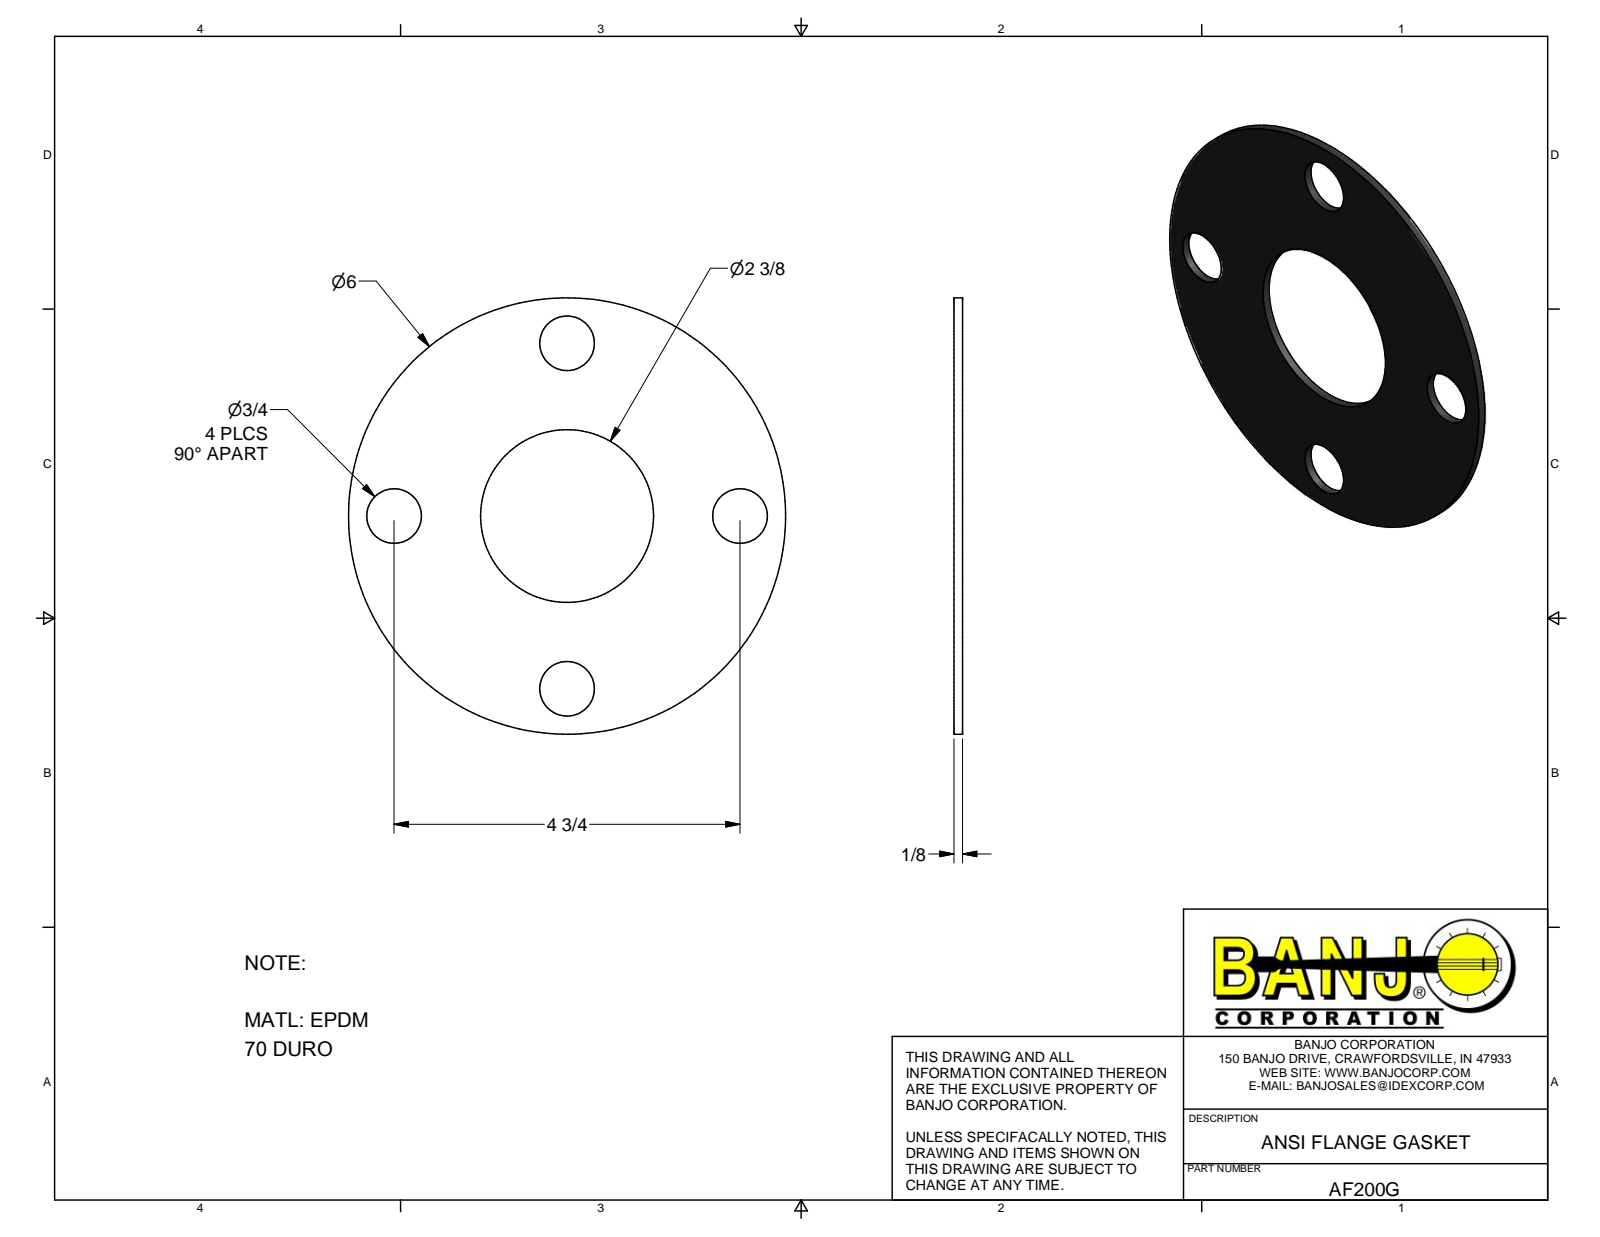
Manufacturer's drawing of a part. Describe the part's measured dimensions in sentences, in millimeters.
The part is named "AF200G". Its 3-D file was written by "Autodesk Inventor 2014 (AUTOMOTIVE_DESIGN)". It is 1 solid with 8 faces: 2 planar, 6 cylindrical and 0 other. Overall it measures 152.4 by 152.4 by 3 millimeters. Its volume is 42 690 cubic millimeters and its surface area 31 207 square millimeters. Round holes: 4 of diameter 19.05, 1 of diameter 60.32. Round bosses or shafts: 1 of diameter 152.4. The main face-to-face distances are 3. The hole center spacings are 60.32, 85.31, 120.64.
